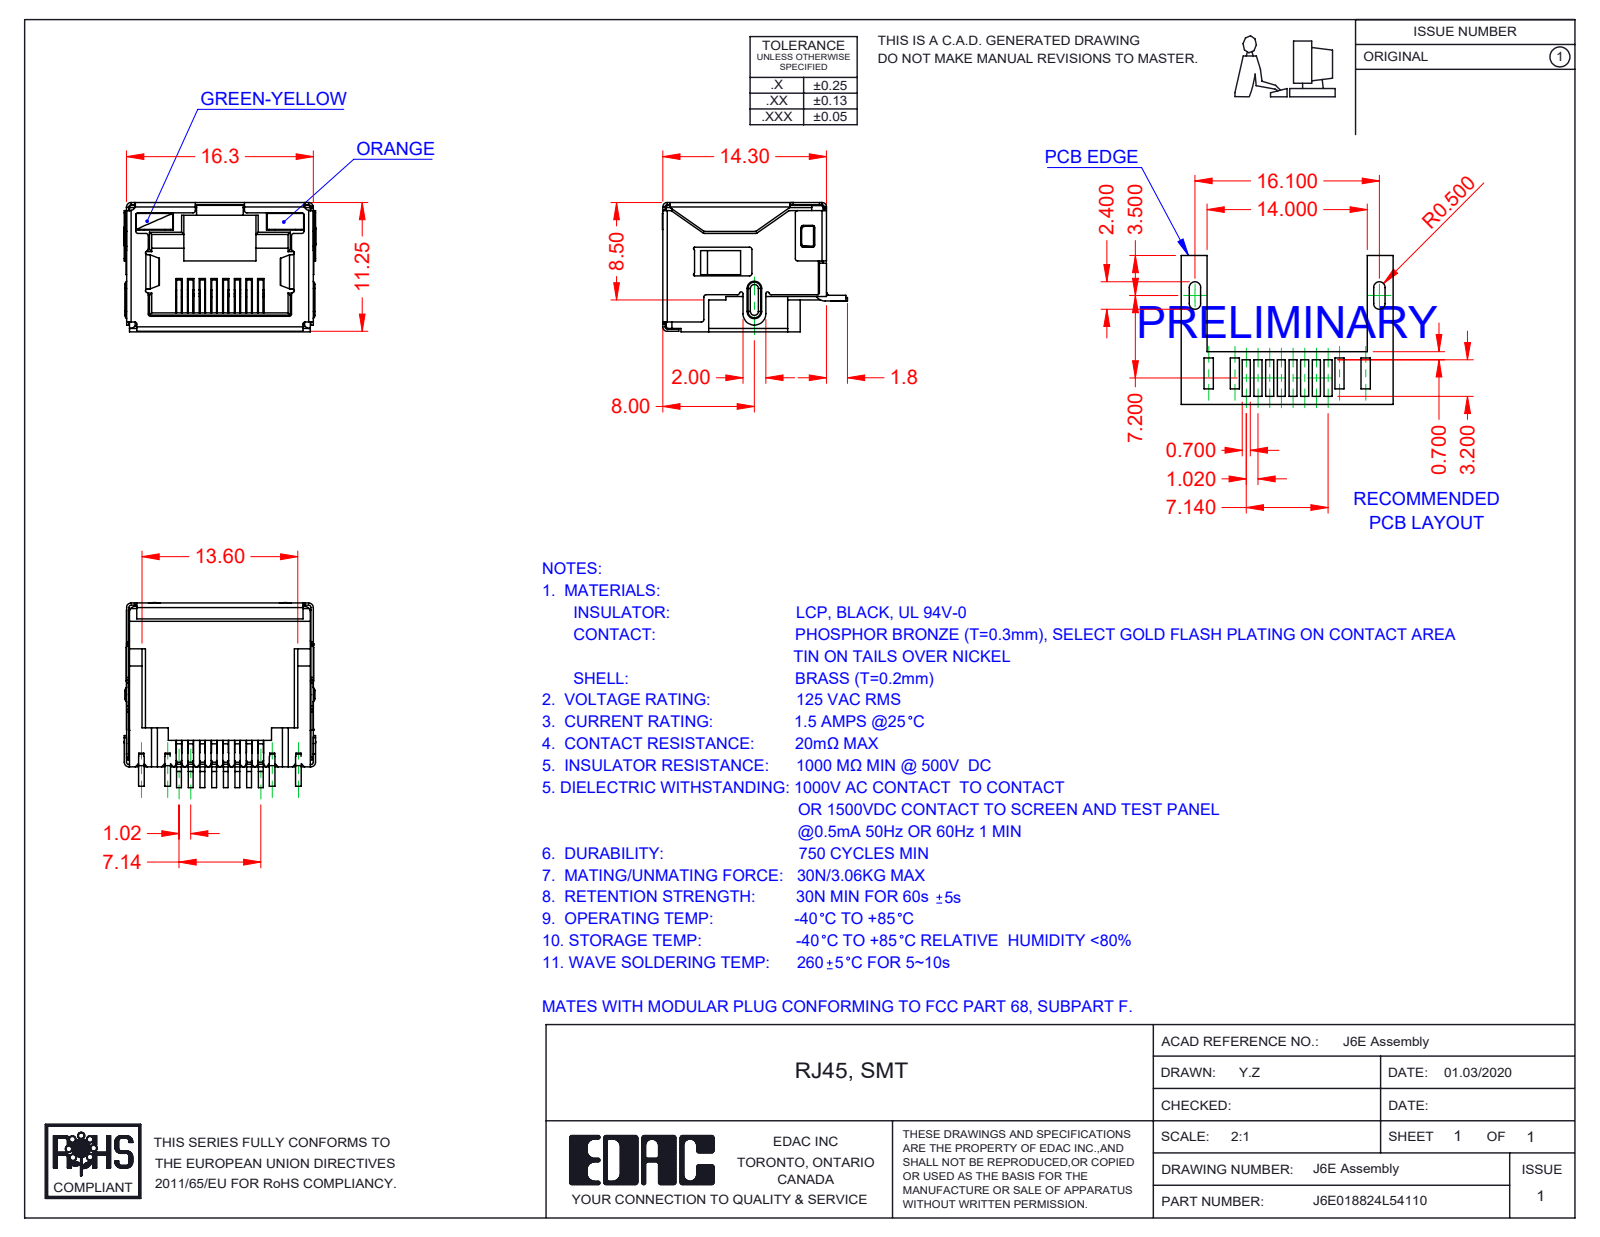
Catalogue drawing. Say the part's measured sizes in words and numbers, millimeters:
The part is named "6E LED RH_4-Orange; 6E LED LH_5-Green-Yellow; 6E Insulator_LED; 6E Shield_LED (+2 more)". Its 3-D file was written by "SolidWorks 2016 (CONFIG_CONTROL_DESIGN)". It is 12 solids with 1498 faces: 1099 planar, 349 cylindrical and 50 other. Overall it measures 16.75 by 16.15 by 11.3 millimeters. Its volume is 1 109 cubic millimeters and its surface area 4 045 square millimeters. Partial cylindrical surfaces (rounded edges, fillets, slot ends): 82 of radius 0.2, 17 of radius 0.25, 13 of radius 0.4, 13 of radius 0.5, 10 of radius 0.1, 7 of radius 0.15, 4 of radius 0.3, 3 of radius 1. The main face-to-face distances are 11.05, 16.05, 16.1, 15.85, 11.1, 11.3, 2.4, 0.7, 9.85, 0.49.
